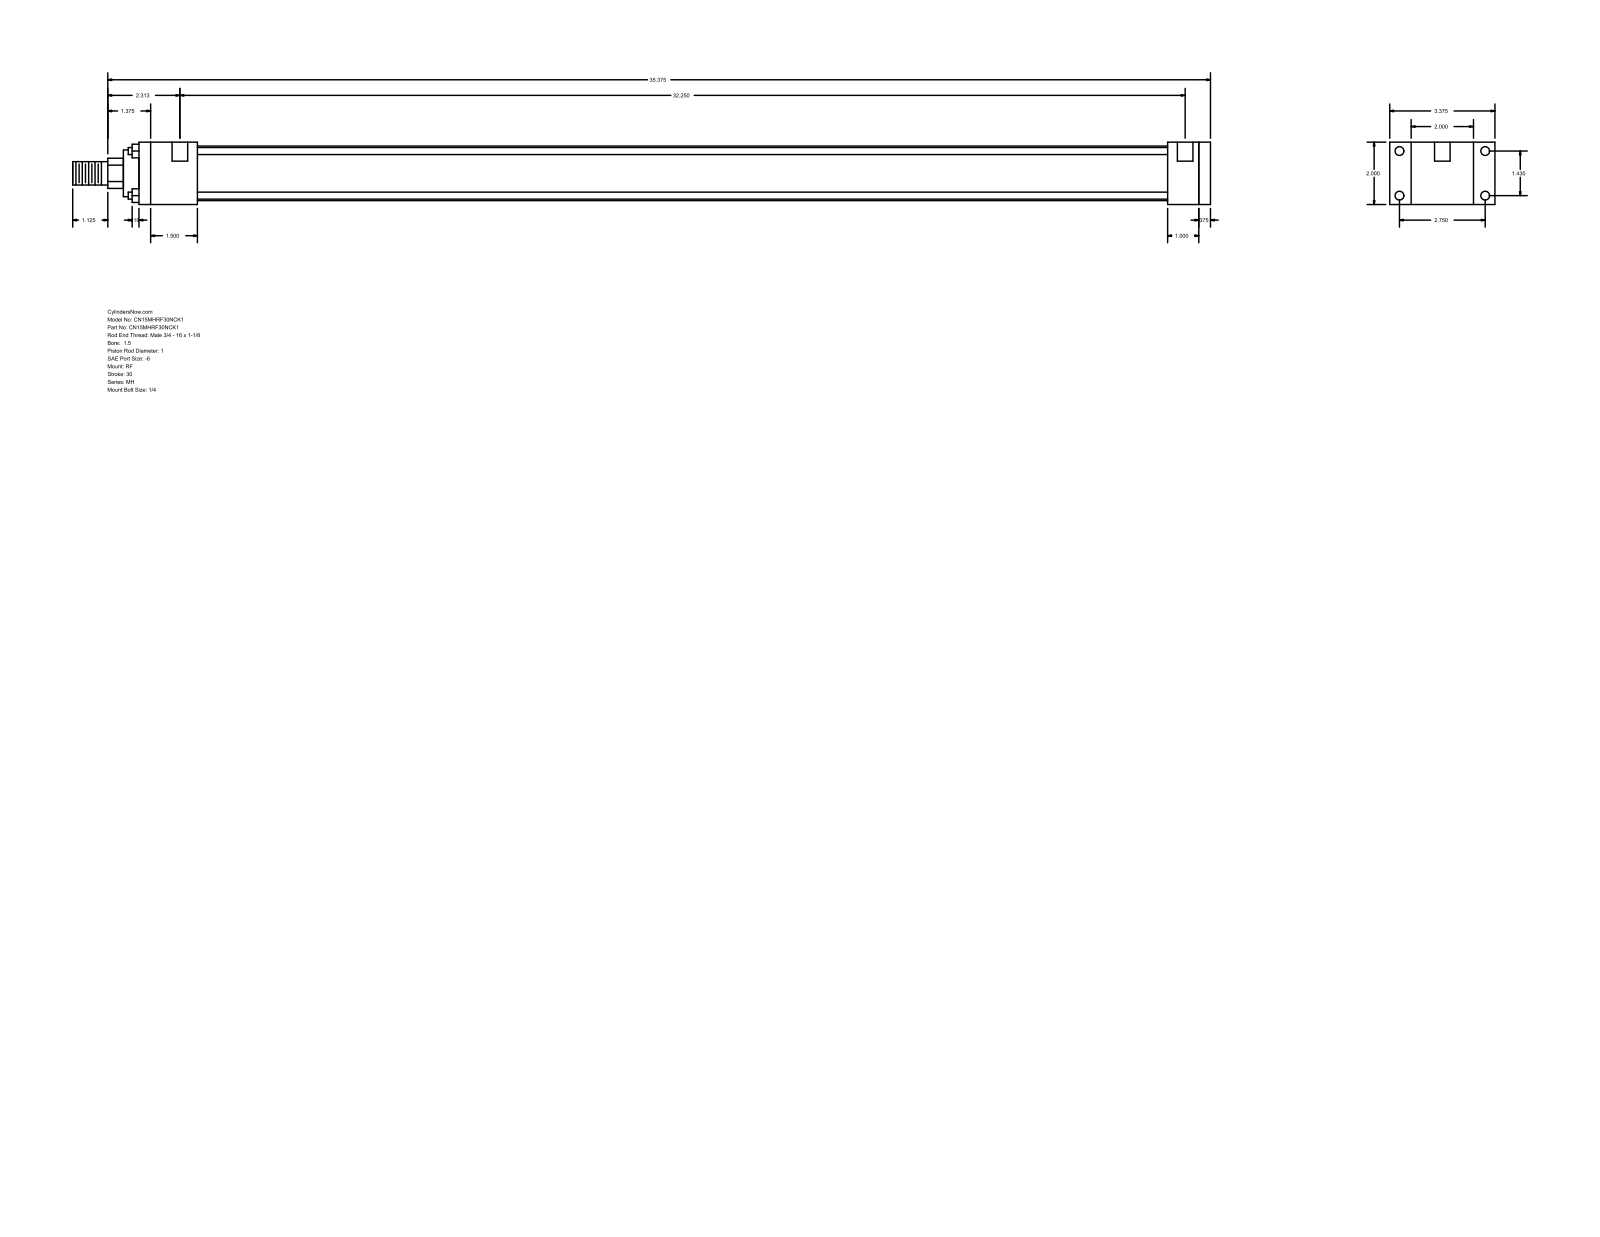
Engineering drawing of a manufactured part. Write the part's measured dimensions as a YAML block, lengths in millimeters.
part_name: "MH_RF__0150_1"
step_written_by: "GSSL Pune (CONFIG_CONTROL_DESIGN)"
units: millimeters
bodies: {solids: 0, faces: 92, planar: 64, cylindrical: 28, other: 0}
overall_size: [927.1, 85.72, 50.8]
round_holes:
  - {diameter: 5.56, count: 4}
  - {diameter: 7.14, count: 4}
  - {diameter: 12.7, count: 2}
round_bosses_or_shafts:
  - {diameter: 5.71, count: 4}
  - {diameter: 44.45, count: 1}
  - {diameter: 38.1, count: 1}
  - {diameter: 25.4, count: 1}
  - {diameter: 19.05, count: 1}
partial_cylinders:
  - {radius: 12.29, count: 1}
face_to_face_distances: [50.8, 9.52, 863.6, 25.4, 873.12, 17.46, 68.26, 838.2, 34.92, 47.63]
hole_center_spacings: [36.32, 69.84, 78.72, 822.33, 3.18, 819.15]
